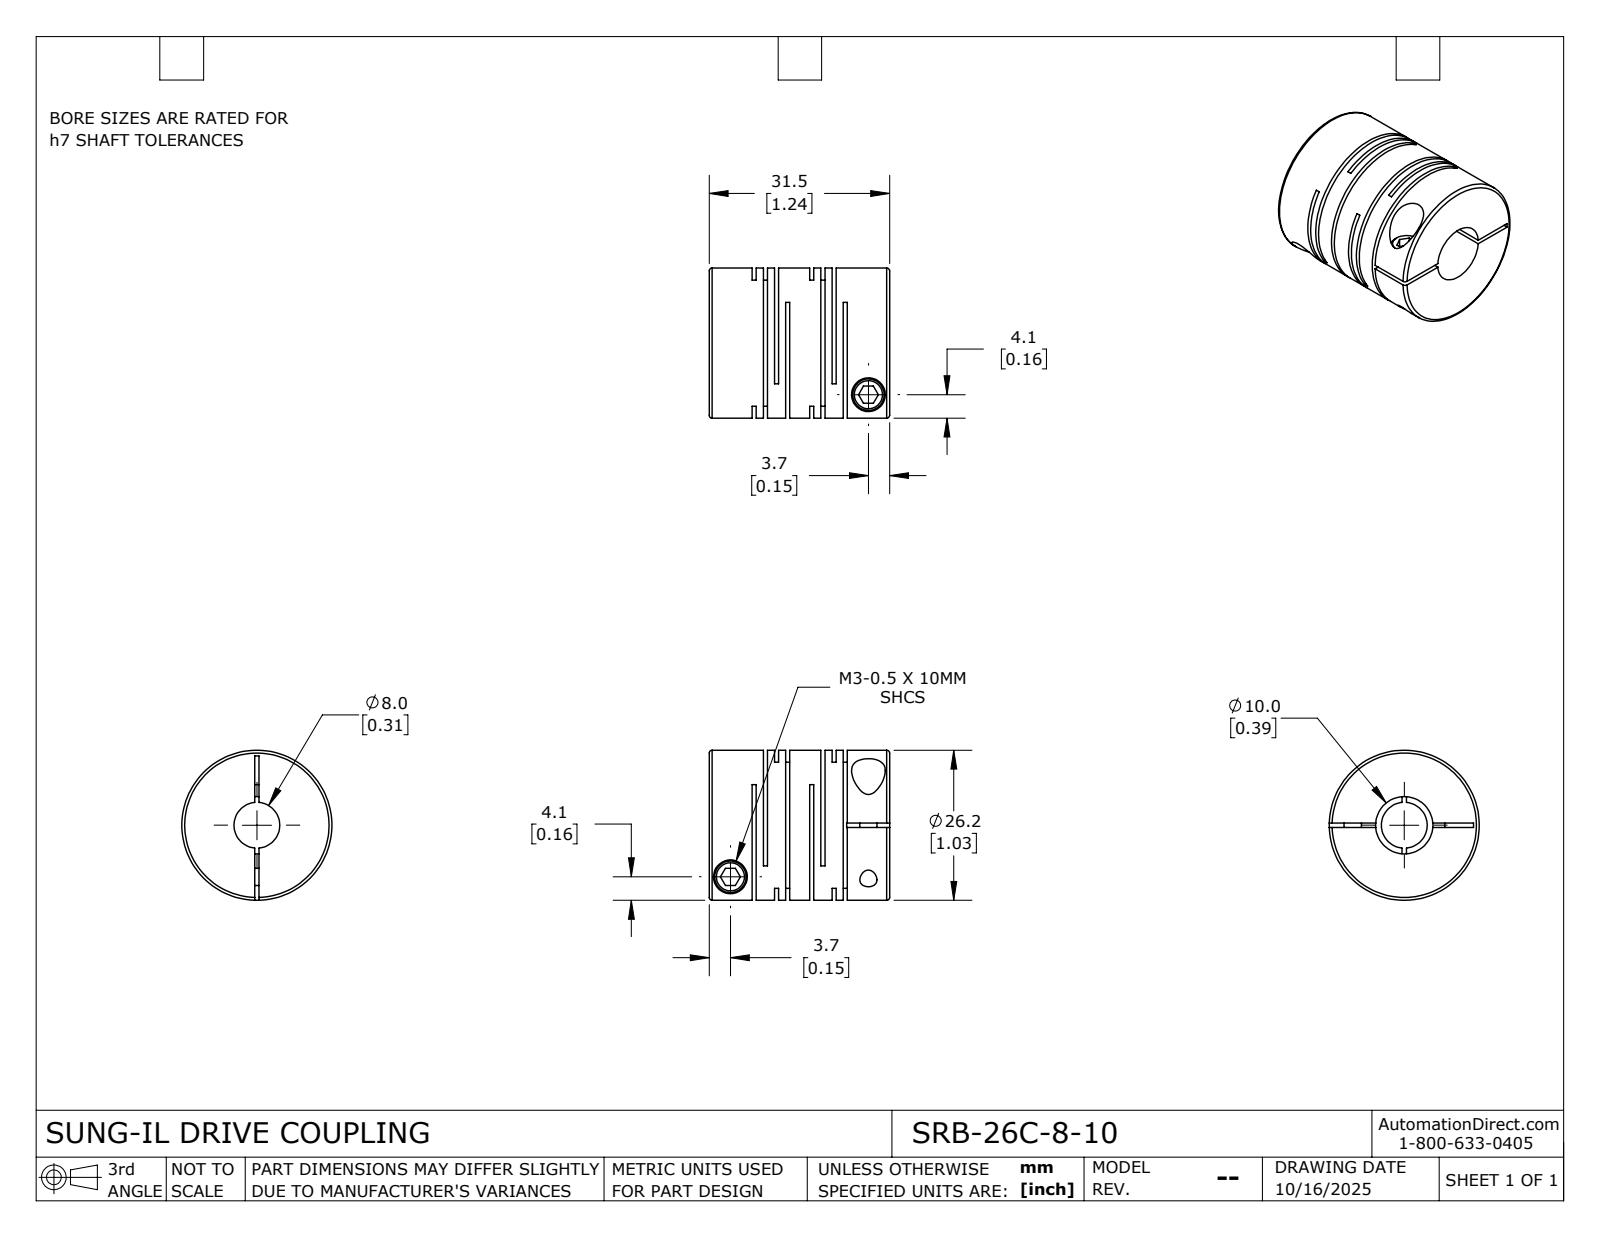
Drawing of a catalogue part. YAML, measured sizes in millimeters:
part_name: "SRB-26C-8-10"
step_written_by: "SolidWorks 2024 (CONFIG_CONTROL_DESIGN)"
units: millimeters
bodies: {solids: 1, faces: 115, planar: 60, cylindrical: 42, other: 13}
overall_size: [31.5, 26.2, 26.2]
volume: 12142
surface_area: 10760
round_holes:
  - {diameter: 3, count: 2}
  - {diameter: 5.9, count: 2}
  - {diameter: 8, count: 1}
  - {diameter: 10, count: 1}
round_bosses_or_shafts:
  - {diameter: 5.5, count: 2}
  - {diameter: 26.2, count: 1}
face_to_face_distances: [1.95, 10.05, 0.71, 3.9, 8.1, 12, 1.24, 2.66, 9.34, 13.95]
